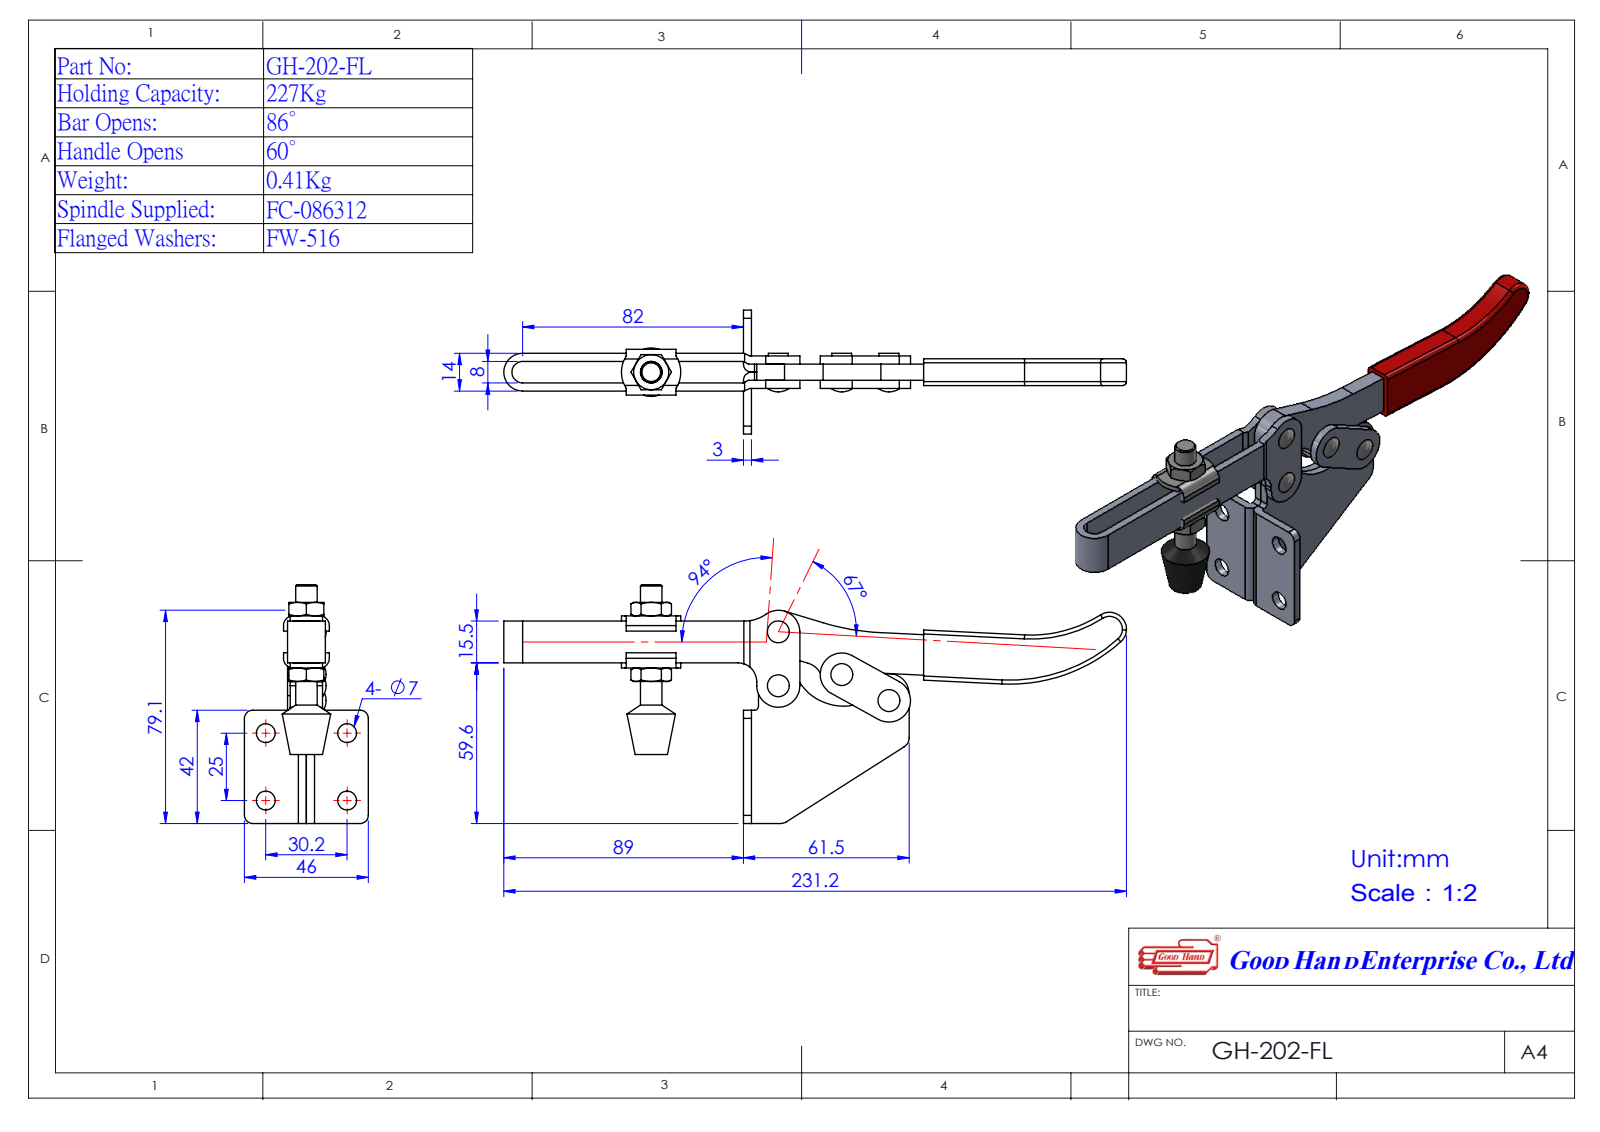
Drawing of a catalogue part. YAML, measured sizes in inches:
part_name: "Group2^GH-202-FL(簡化); GH-202-FL(簡化); Group1^GH-203-FL(簡化); Group5^GH-202-FL(簡化) (+2 more)"
step_written_by: "SolidWorks 2016 (AUTOMOTIVE_DESIGN)"
units: inches
bodies: {solids: 5, faces: 252, planar: 107, cylindrical: 107, other: 38}
overall_size: [9.102, 3.488, 1.811]
volume: 3.739
surface_area: 53.17
round_holes:
  - {diameter: 0.197, count: 4}
  - {diameter: 0.276, count: 4}
  - {diameter: 0.249, count: 1}
round_bosses_or_shafts:
  - {diameter: 0.289, count: 4}
  - {diameter: 0.312, count: 1}
  - {diameter: 0.197, count: 1}
partial_cylinders:
  - {radius: 0.118, count: 7}
  - {radius: 0.315, count: 6}
  - {radius: 0.047, count: 4}
  - {radius: 0.142, count: 4}
  - {radius: 0.157, count: 3}
  - {radius: 0.276, count: 2}
  - {radius: 0.435, count: 2}
  - {radius: 0.059, count: 1}
face_to_face_distances: [0.039, 0.079, 0.118, 0.394, 0.433, 0.354, 0.236, 0.315, 0.472, 0.157]
hole_center_spacings: [0.984, 1.189, 1.544, 0.785, 0.787, 0.942, 1.118, 1.629]
